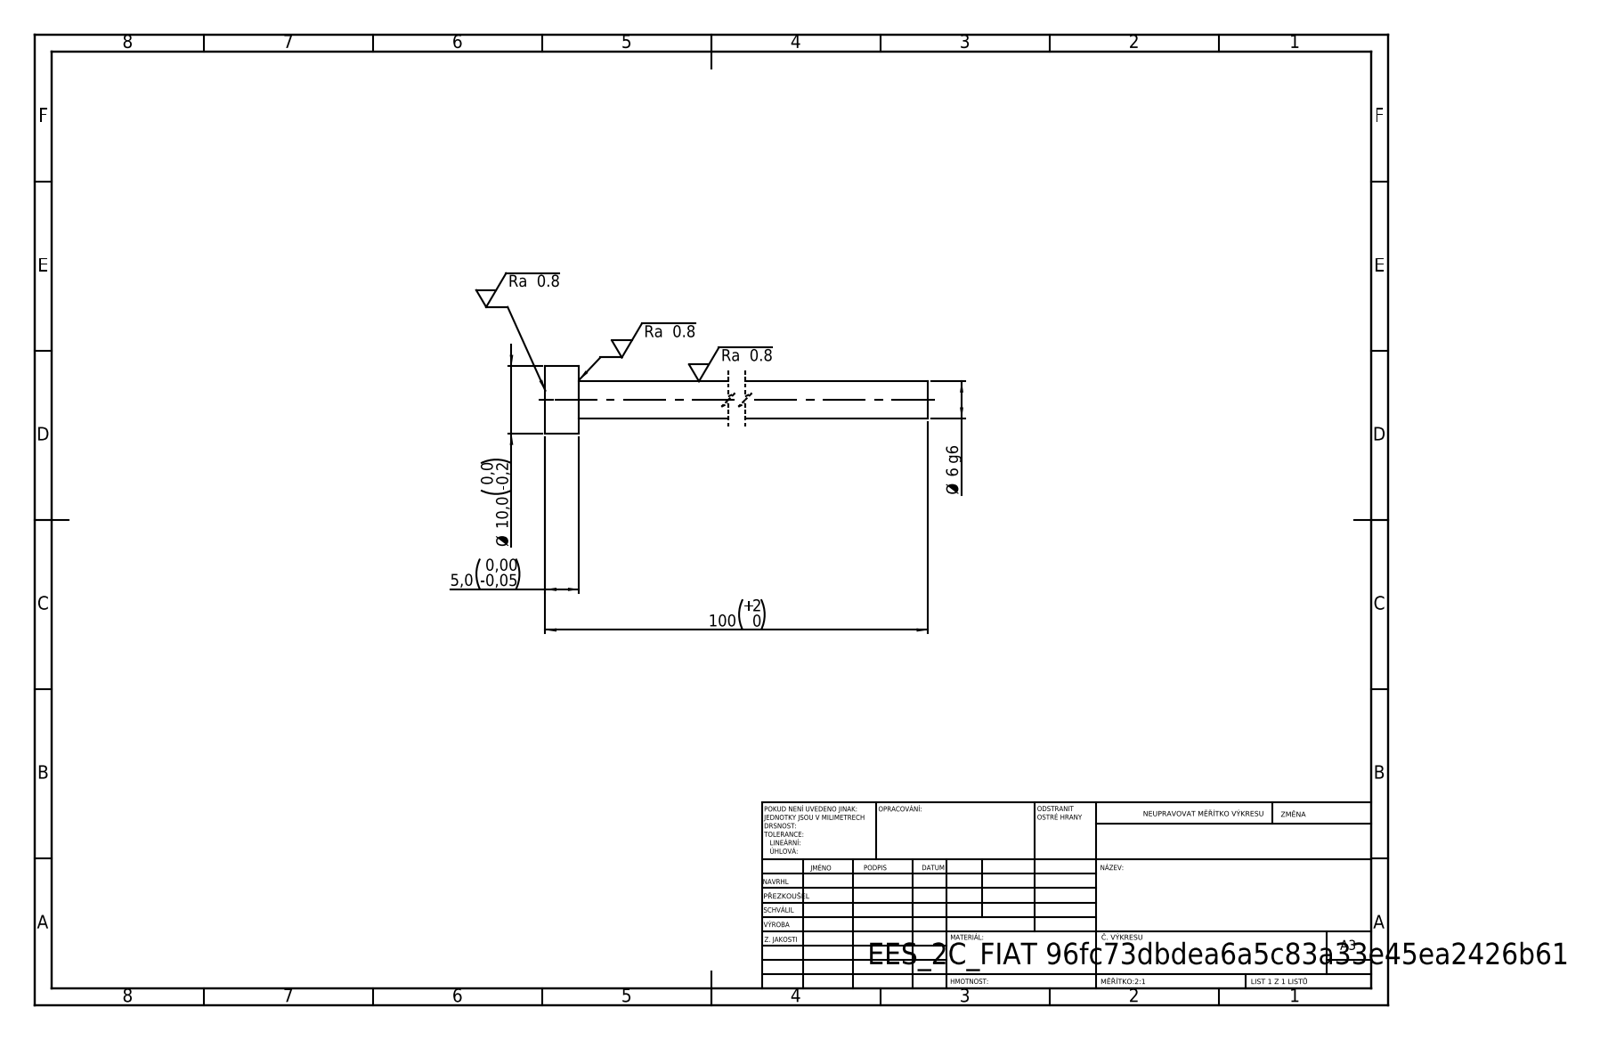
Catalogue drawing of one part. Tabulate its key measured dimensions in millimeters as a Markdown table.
| quantity | value |
| --- | --- |
| STEP written by | SolidWorks 2019 (CONFIG_CONTROL_DESIGN) |
| units | millimeters |
| bodies | 1 solid, 7 faces (3 planar, 4 cylindrical, 0 other) |
| overall size | 100 × 10 × 10 |
| volume | 2 650 mm³ |
| surface area | 1 956 mm² |
| round bosses / shafts (diameter × count) | 10 × 1, 5.5 × 1 |
| main face-to-face distances | 5, 100, 95 |
